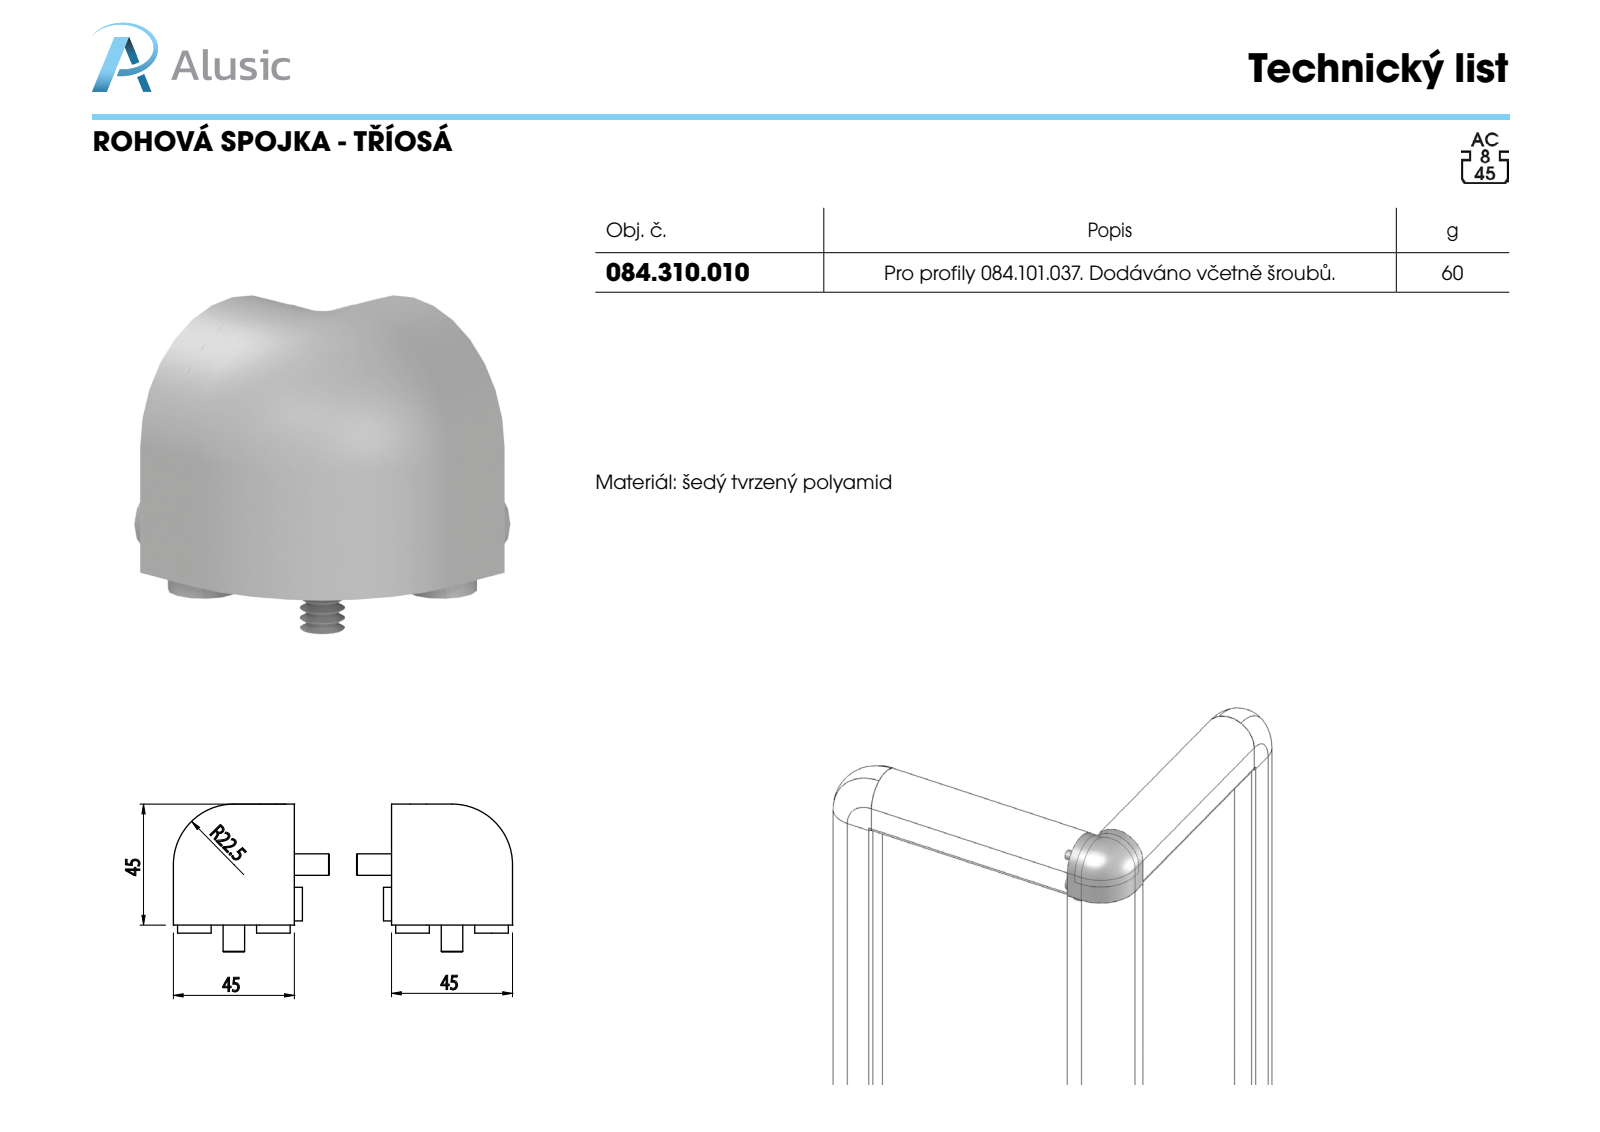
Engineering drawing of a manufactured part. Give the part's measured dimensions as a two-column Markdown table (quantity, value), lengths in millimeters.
| quantity | value |
| --- | --- |
| part name | 084.310.010; 084.310.010-2; 084.301.000 VITI ALUSIC_084.301.003; 084.310.010-1 |
| STEP written by | SolidWorks 2011 (CONFIG_CONTROL_DESIGN) |
| units | millimeters |
| bodies | 5 solids, 177 faces (95 planar, 68 cylindrical, 14 other) |
| overall size | 58 × 58 × 55 |
| volume | 42 454 mm³ |
| surface area | 26 338 mm² |
| round holes (diameter × count) | 3 × 3, 10 × 3, 8.5 × 1, 13.5 × 1 |
| round bosses / shafts (diameter × count) | 12.5 × 7, 13 × 3, 8 × 3, 19.5 × 1, 14.5 × 1 |
| partial cylindrical surfaces (radius × count) | 4.25 × 2, 8 × 2, 19.5 × 2, 22.5 × 2, 1 × 1, 29 × 1, 32 × 1 |
| main face-to-face distances | 3, 7, 10, 13, 6, 16, 45, 35, 38, 48 |
| hole center spacings | 20.79, 1.93, 21.64, 28.71, 29.4, 30.5, 31.21, 42.39 |
